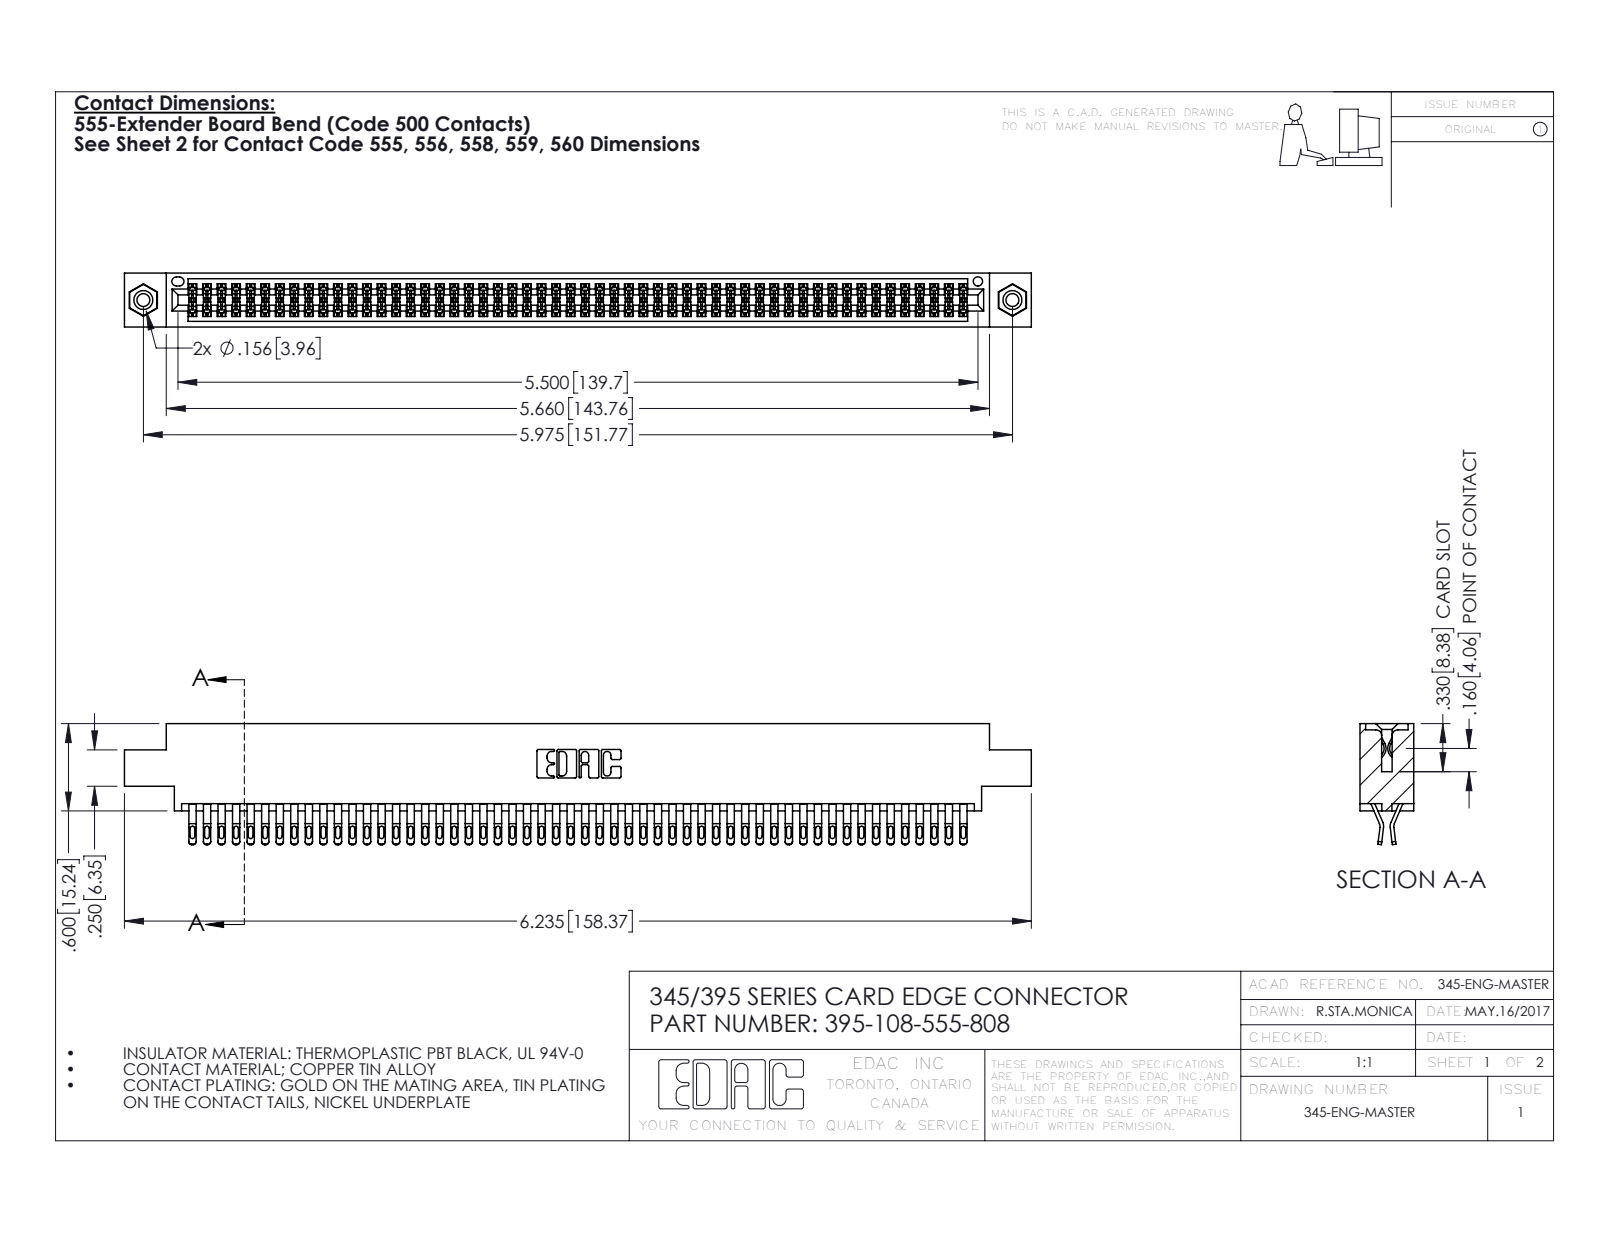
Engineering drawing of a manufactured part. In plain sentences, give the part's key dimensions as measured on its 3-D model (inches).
The part is named "345 Part_0.170 Offset - 0.156 Dia-TI; 395-108-555-808; 345-250-001_345-250-003-102; 345-292-001_555 Tail". Its 3-D file was written by "SolidWorks 2016 (CONFIG_CONTROL_DESIGN)". It is 111 solids with 6238 faces: 3464 planar, 2758 cylindrical and 16 other. Overall it measures 6.235 by 0.832 by 0.37 inches. Its volume is 0.957 cubic inches and its surface area 38.24 square inches. Round holes: 2 of diameter 0.089, 2 of diameter 0.125, 2 of diameter 0.156, 1 of diameter 0.064. Round bosses or shafts: 2 of diameter 0.155. Partial cylindrical surfaces (rounded edges, fillets, slot ends): 270 of radius 0.016, 216 of radius 0.02, 162 of radius 0.006, 22 of radius 0.01, 6 of radius 0.007, 6 of radius 0.031, 3 of radius 0.026, 2 of radius 0.01. The main face-to-face distances are 0.072, 0.298, 0.37, 0.025, 0.2, 0.098, 0.272, 0.225, 0.175, 0.149. The hole center spacings are 0.27, 5.739, 5.975.
